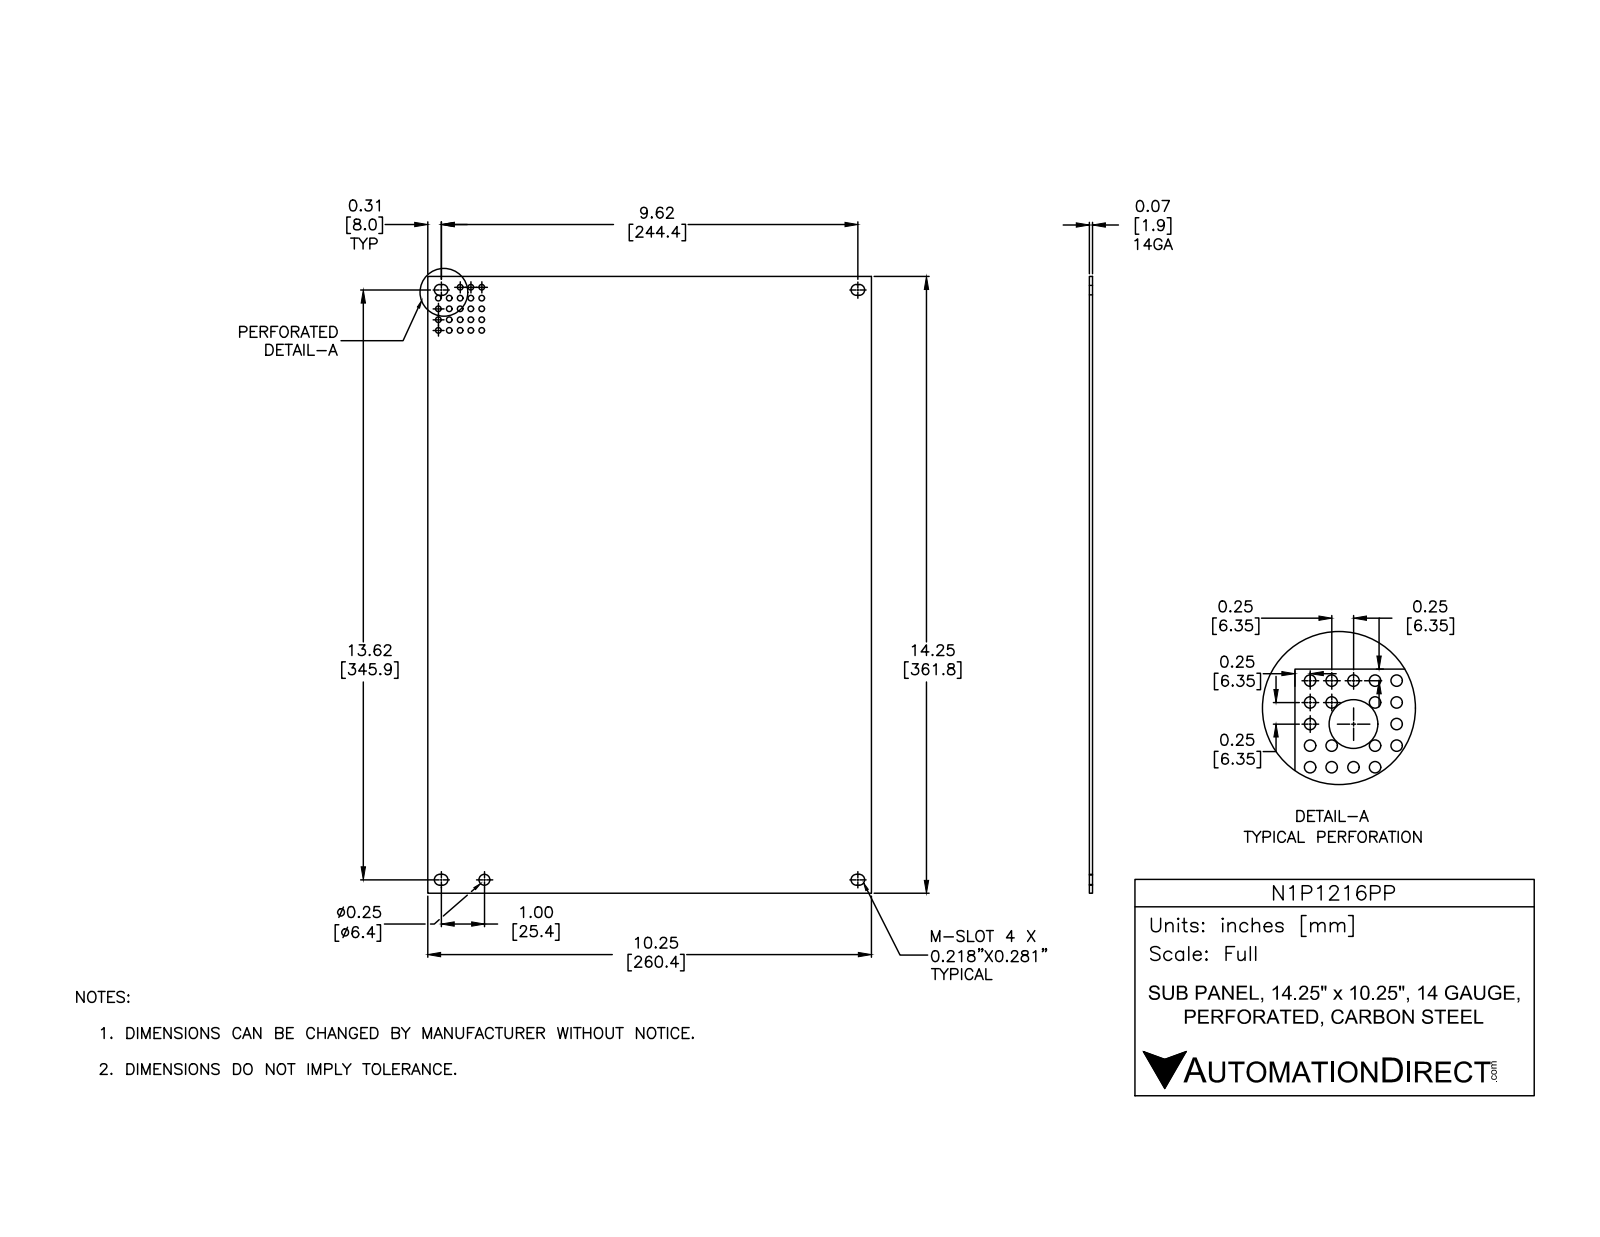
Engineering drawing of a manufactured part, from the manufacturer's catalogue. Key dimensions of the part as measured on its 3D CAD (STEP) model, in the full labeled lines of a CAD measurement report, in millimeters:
Part name (STEP PRODUCT): N1P1216PP
STEP written by: Autodesk Inventor 2012 (AUTOMOTIVE_DESIGN)
Units: millimetres
Bodies: 1 solid, 23 faces (14 planar, 9 cylindrical, 0 other)
Overall size (bounding box): 362 × 260.4 × 1.9
Volume: 176 800 mm³ · Surface area: 190 600 mm²
Round holes (diameter × count): ⌀6.4 ×1
Partial cylindrical surfaces — rounded edges, fillets, slot ends (radius × count): R3.2 ×8
Main face-to-face distances: 1.9, 260.4, 362, 11.1, 350.8, 4.8, 357.2, 6.4, 346, 339.7
